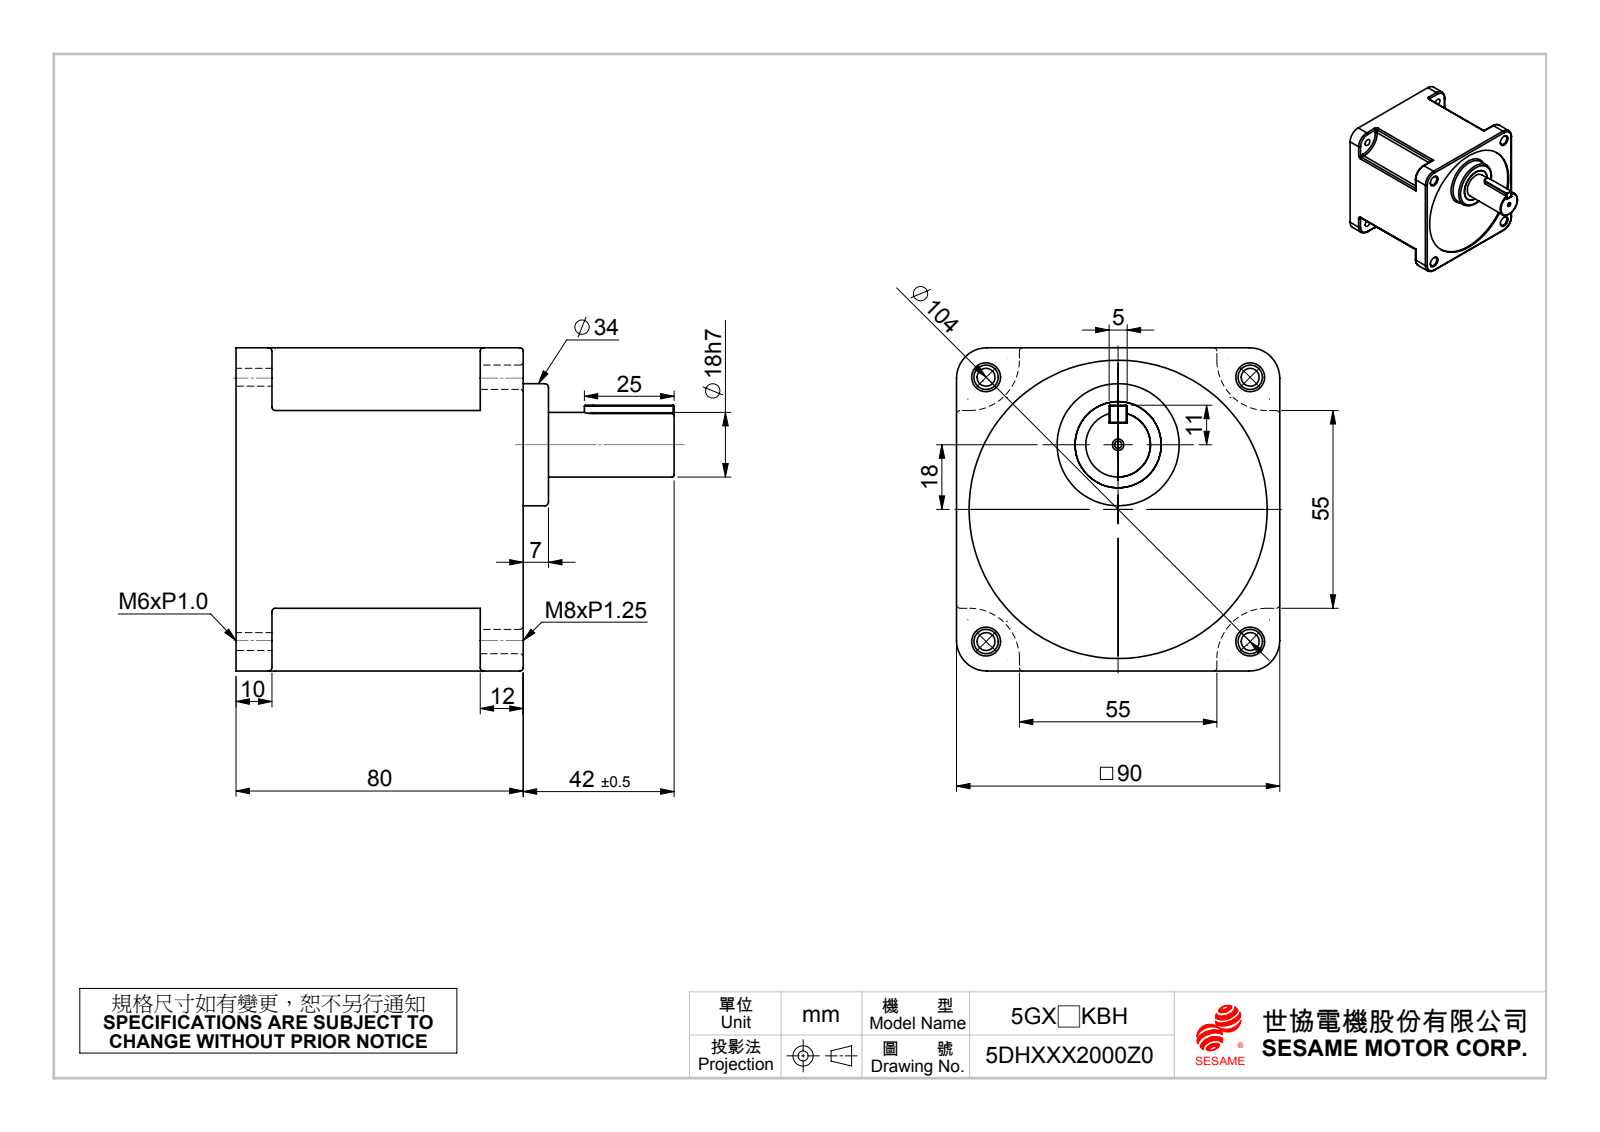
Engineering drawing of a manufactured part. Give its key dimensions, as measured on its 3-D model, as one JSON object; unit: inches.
{"part_name": "18x24x4; 5GX側板成品; 5x5xL_25L", "step_written_by": "SolidWorks 2010 (CONFIG_CONTROL_DESIGN)", "units": "inches", "bodies": {"solids": 8, "faces": 220, "planar": 65, "cylindrical": 104, "other": 51}, "overall_size": [4.803, 3.543, 3.543], "volume_in3": 34.94, "surface_area_in2": 143.9, "round_holes": [[0.197, 4], [0.268, 4], [0.079, 1], [0.709, 1], [0.882, 1], [0.945, 1], [3.267, 1], [3.268, 1]], "round_bosses_or_shafts": [[0.551, 3], [3.26, 1], [2.756, 1], [1.339, 1], [0.787, 1], [0.748, 1], [0.63, 1]], "partial_cylinders_radius": [[0.039, 24], [0.335, 4], [0.551, 4], [0.098, 1]], "face_to_face_distances": [0.063, 0.047, 0.126, 3.543, 0.11, 0.173, 2.941, 2.894, 2.831, 2.768], "hole_center_spacings": [2.047, 2.895, 1.625, 2.597, 4.094, 0.709]}
